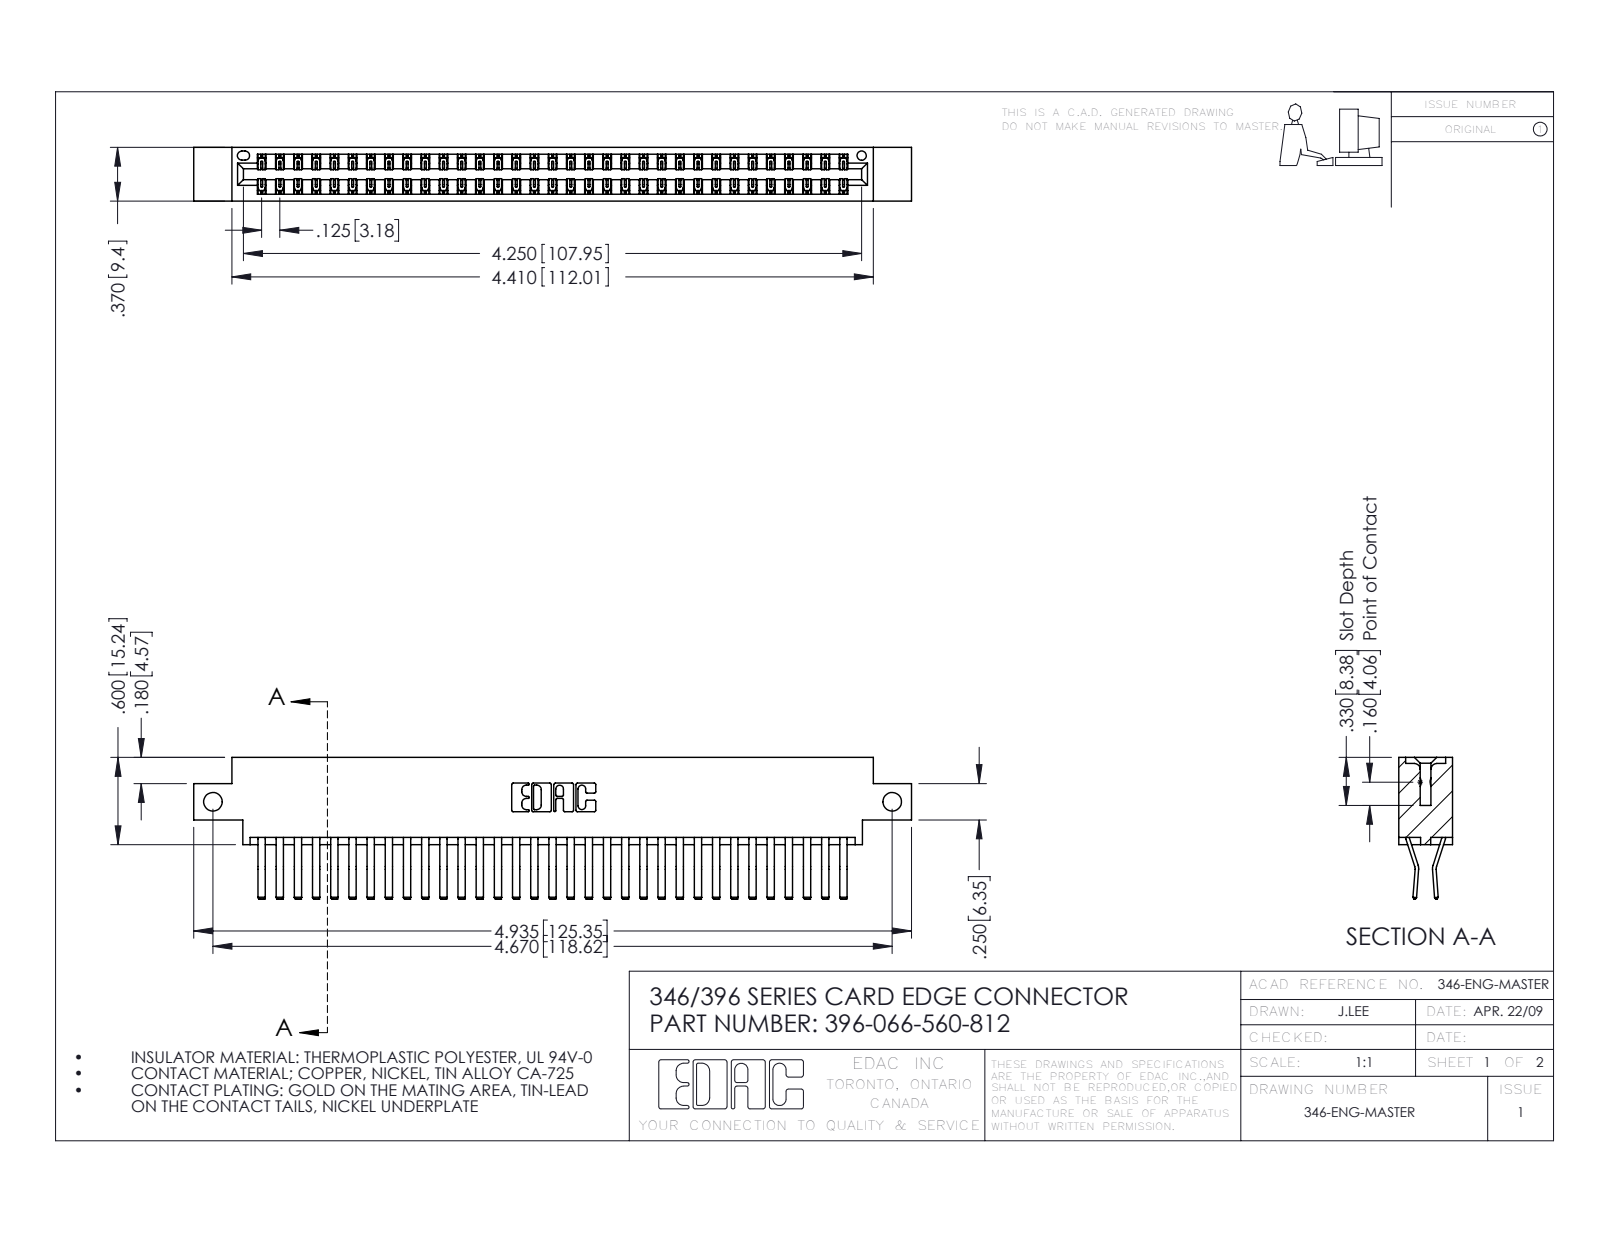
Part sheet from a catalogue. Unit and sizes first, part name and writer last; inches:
Units: inches
Overall size (bounding box): 4.935 × 0.975 × 0.37
Round holes (diameter × count): ⌀0.128 ×2, ⌀0.064 ×1
Partial cylindrical surfaces — rounded edges, fillets, slot ends (radius × count): R0.006 ×99, R0.01 ×22, R0.007 ×6, R0.031 ×6, R0.026 ×3, R0.01 ×2, R0.014 ×2, R0.022 ×2
Main face-to-face distances: 0.048, 0.322, 0.37, 0.025, 0.25, 0.072, 0.298, 0.275, 0.148, 0.222
Hole centre spacings: 4.67
Volume: 0.753 in³ · Surface area: 27.93 in²
Bodies: 67 solids, 3690 faces (2390 planar, 1300 cylindrical, 0 other)
Part name (STEP PRODUCT): 396-066-560-812; 345-292-001_560 Tail; 346 Part_0.170 Offset - Side Mount
STEP written by: SolidWorks 2016 (CONFIG_CONTROL_DESIGN)
